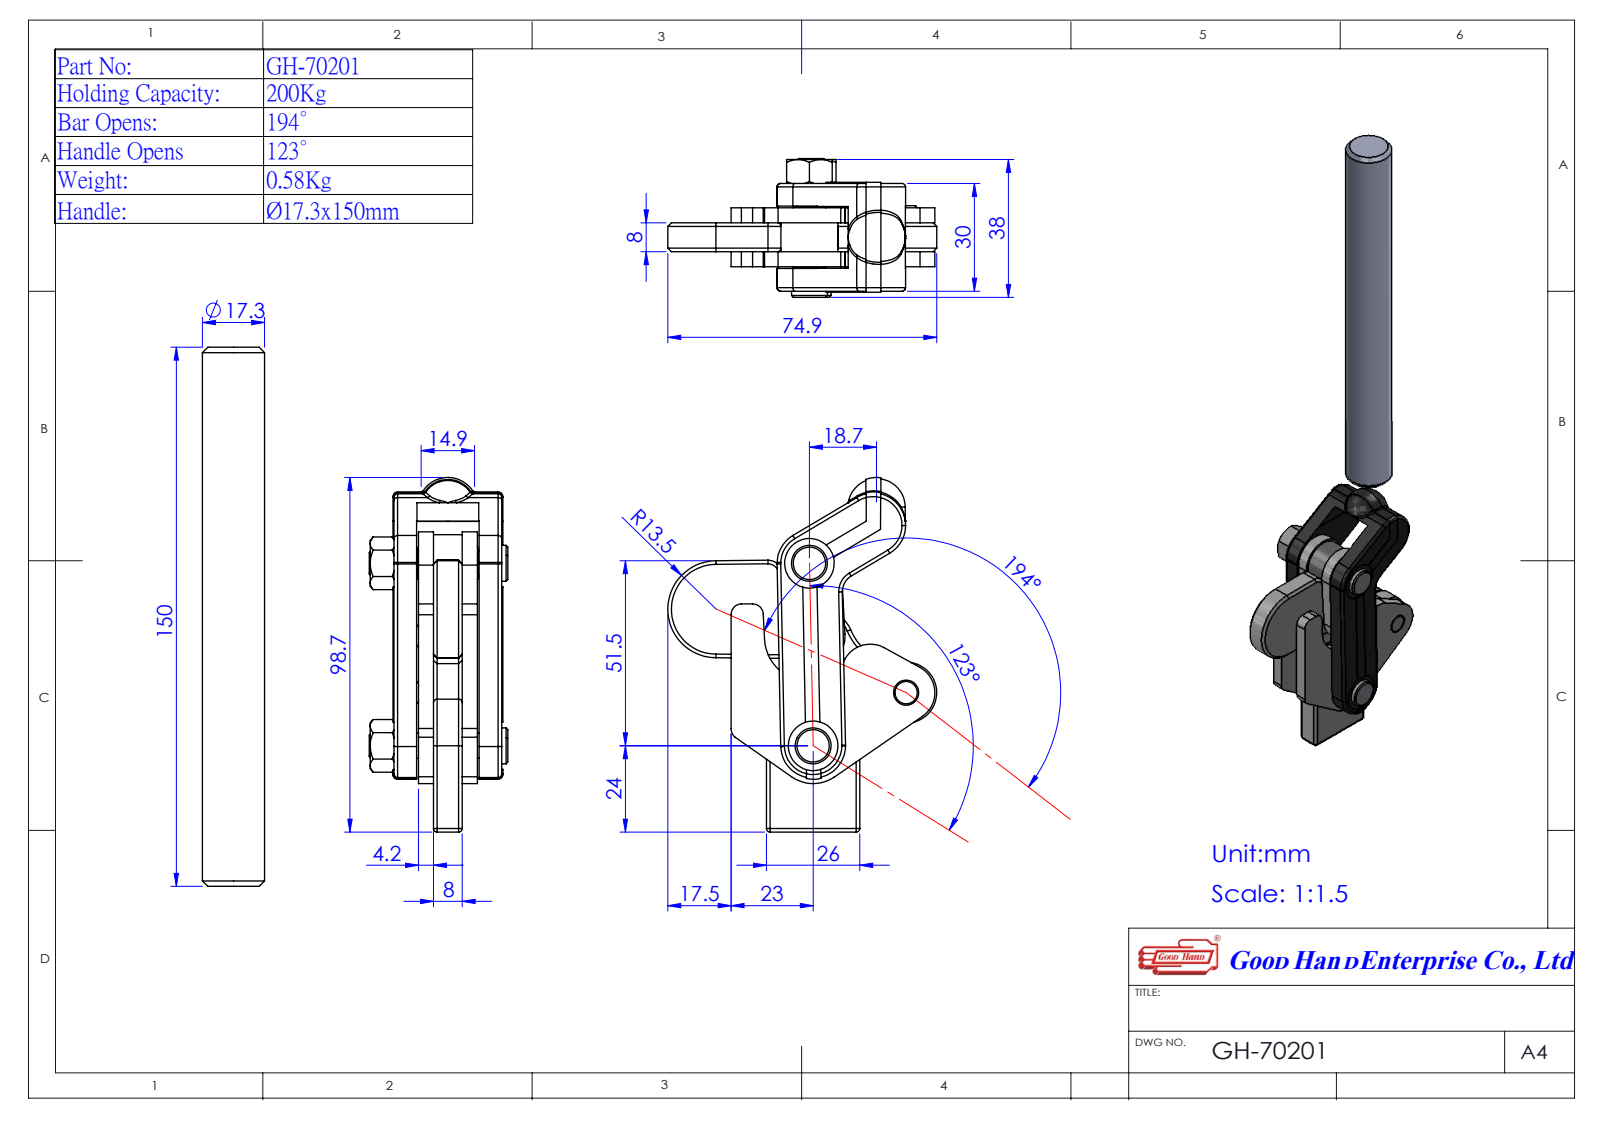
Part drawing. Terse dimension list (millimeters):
name: Group2^GH-70201(簡化); 3700108-1^GH-70201(簡化); Group1^GH-70201(簡化); 1700129-1^GH-70201(簡化) (+3 more)
written by: SolidWorks 2016 (AUTOMOTIVE_DESIGN)
unit: mm
bodies: 6 solids, 288 faces (110 planar, 95 cylindrical, 83 other)
size: 249.97 × 74.86 × 38.6
volume: 75 063 mm³; area: 44 465 mm²
holes: 2× ⌀6.97, 1× ⌀13.9
bosses: 2× ⌀10, 2× ⌀6.97, 1× ⌀17.3, 1× ⌀15.9
rounds: 10× R1, 3× R9, 2× R8, 2× R8.5, 2× R8.75, 2× R9.3, 1× R3, 1× R3
face distances: 8, 4.2, 12.2, 12.7, 0.5, 4.7, 16.9, 16.4, 11, 6.3
hole spacings: 30.56
